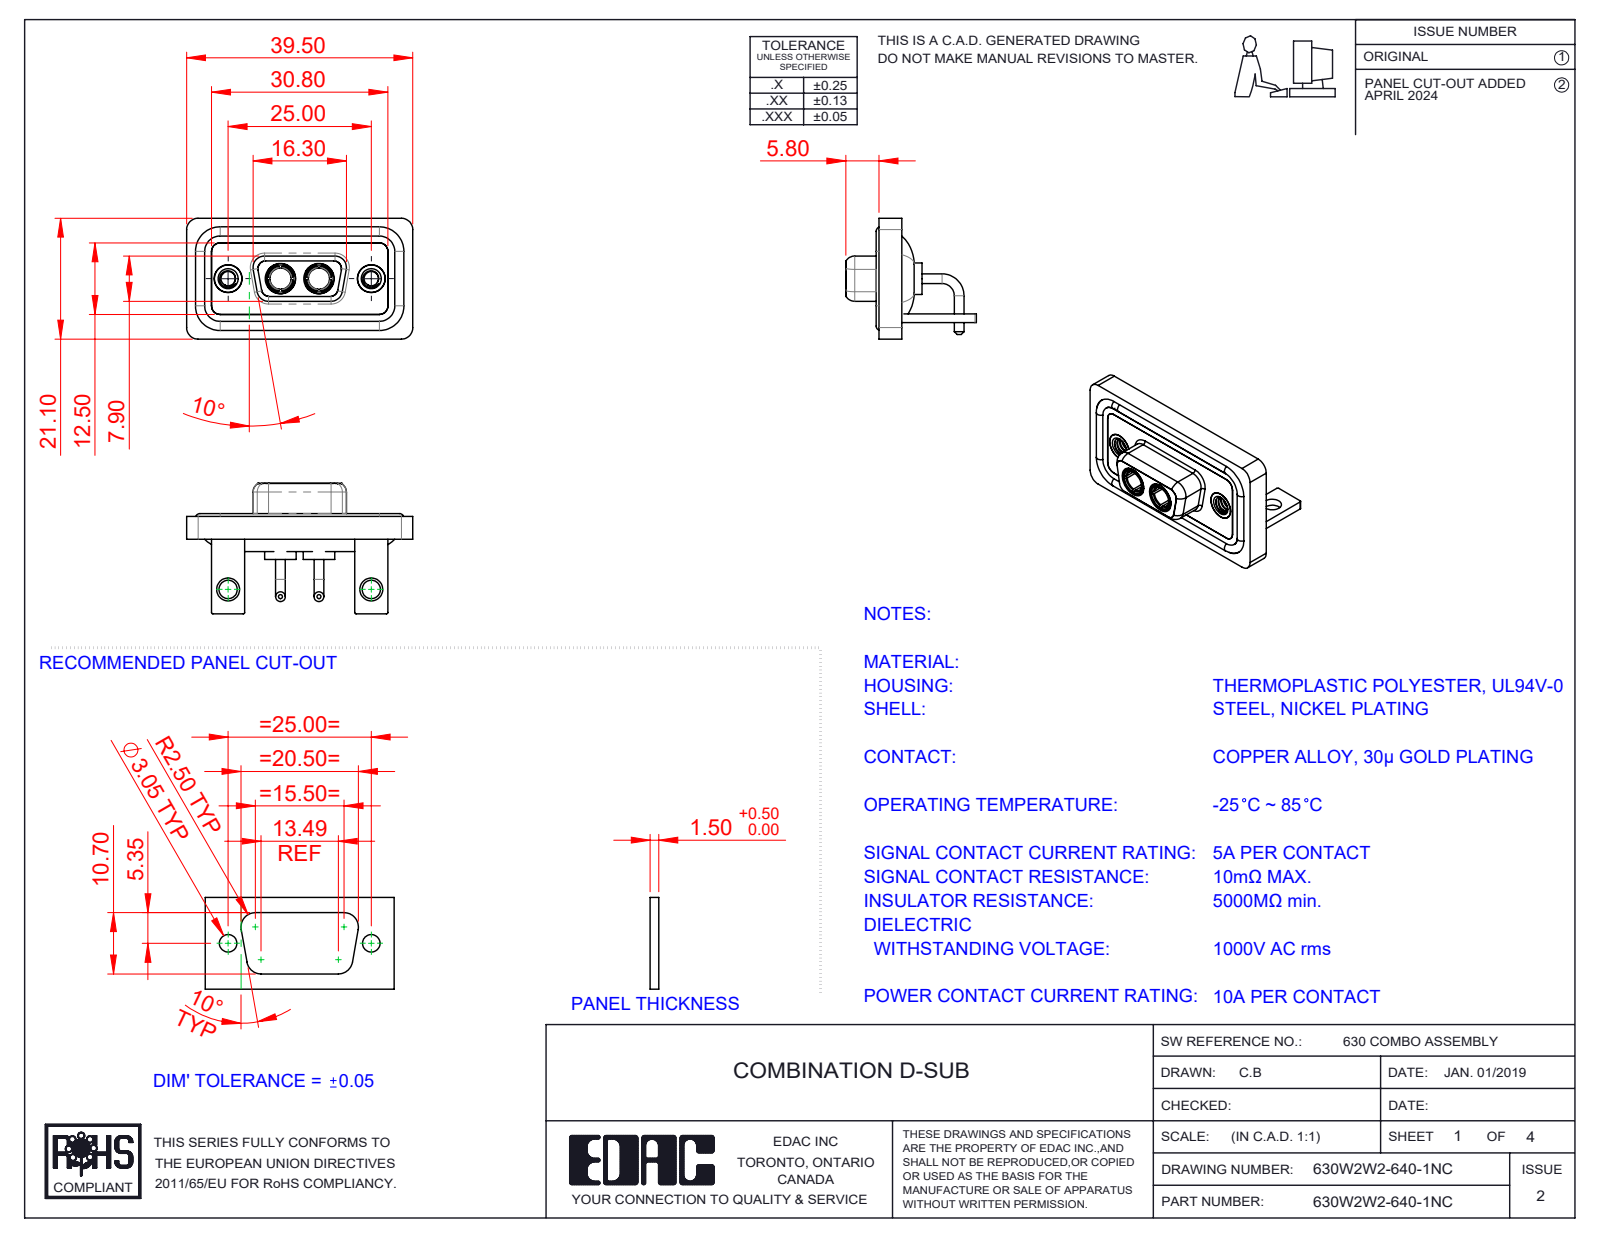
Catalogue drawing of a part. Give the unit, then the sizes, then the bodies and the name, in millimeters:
Units: millimetres
Overall size (bounding box): 39.5 × 22.8 × 21.1
Round holes (diameter × count): ⌀4.85 ×4, ⌀2.5 ×2, ⌀3.2 ×2, ⌀3.7 ×2, ⌀4 ×2, ⌀4.05 ×2, ⌀5 ×2, ⌀5.3 ×2
Round bosses / shafts (diameter × count): ⌀1.7 ×4, ⌀1.6 ×4, ⌀5.5 ×2, ⌀5.2 ×2, ⌀4.96 ×2, ⌀4.95 ×2, ⌀4.8 ×2, ⌀4.75 ×2
Partial cylindrical surfaces — rounded edges, fillets, slot ends (radius × count): R2 ×19, R1.5 ×18, R0.25 ×16, R1.35 ×8, R1.6 ×8, R0.5 ×5, R0.6 ×4, R0.65 ×4
Main face-to-face distances: 0.4, 2.9, 1.5, 1.8, 1.1, 3.7, 0.8, 2.5, 1.6, 3.1
Hole centre spacings: 9.14, 15.86, 25, 6.72
Volume: 5 060 mm³ · Surface area: 8 423 mm²
Bodies: 13 solids, 584 faces (183 planar, 260 cylindrical, 141 other)
Part name (STEP PRODUCT): 630Combo Shell Rear_09 Contacts; 630Combo Housing_2W2; 630Combo Stabilizer Bracket_50 Contacts; 630W2W2-640-1NC (+4 more)
STEP written by: SolidWorks 2023 (CONFIG_CONTROL_DESIGN)
